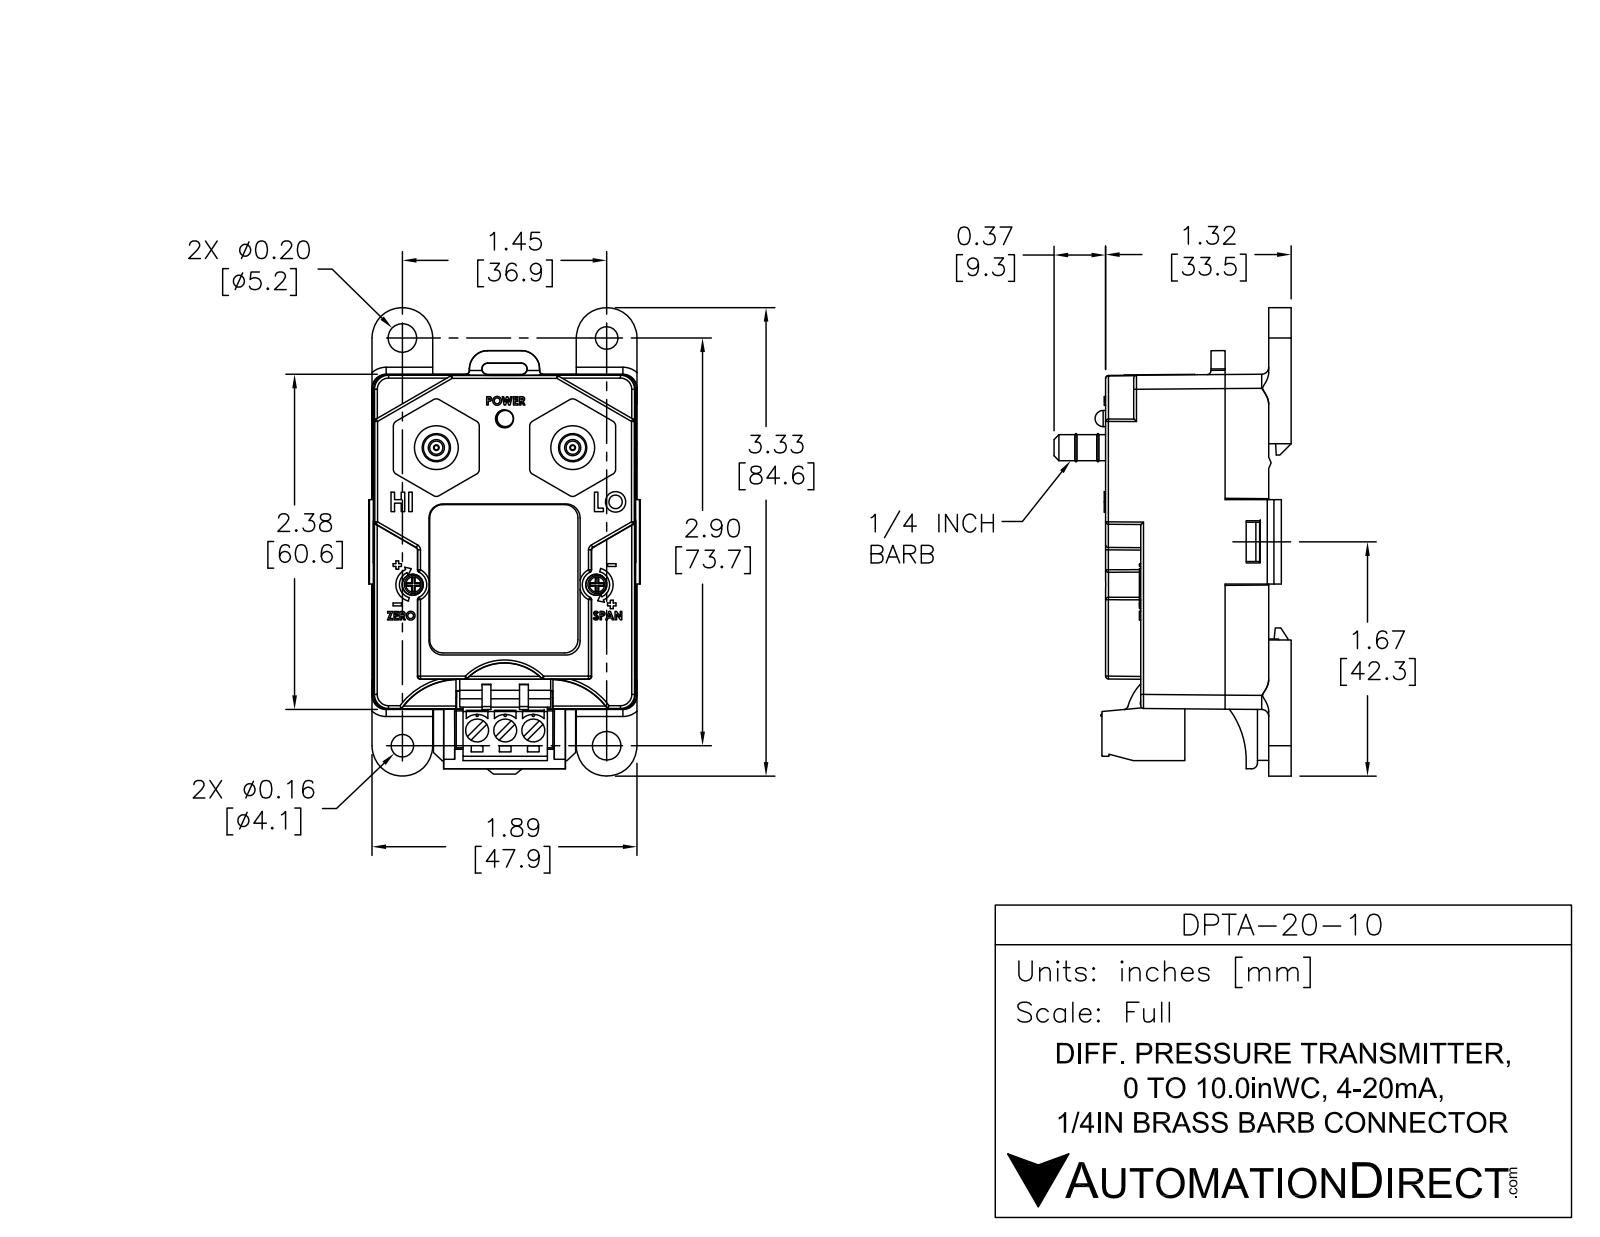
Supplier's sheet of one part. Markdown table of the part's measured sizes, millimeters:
| quantity | value |
| --- | --- |
| part name | DPTA-20-10 |
| STEP written by | SolidWorks 2011 (AUTOMOTIVE_DESIGN) |
| units | millimeters |
| bodies | 11 solids, 448 faces (354 planar, 85 cylindrical, 9 other) |
| overall size | 85.01 × 49.76 × 43.1 |
| volume | 29 684 mm³ |
| surface area | 34 743 mm² |
| round holes (diameter × count) | 4 × 7, 2.5 × 2, 5.12 × 2, 3.1 × 1 |
| round bosses / shafts (diameter × count) | 5 × 3, 3.5 × 3, 3.5 × 3, 8 × 2, 4.75 × 2, 3 × 1 |
| partial cylindrical surfaces (radius × count) | 3 × 12, 2 × 4, 5.5 × 4, 0.99 × 2, 1.06 × 2, 1.12 × 2, 2.38 × 2, 3.25 × 2 |
| main face-to-face distances | 1, 1.9, 4, 29.1, 0.5, 46.9, 5.9, 5, 33.1, 27.2 |
| hole center spacings | 13.55, 20.73, 23.37, 24.92, 29.43, 34.46, 36.67, 38.22 |
